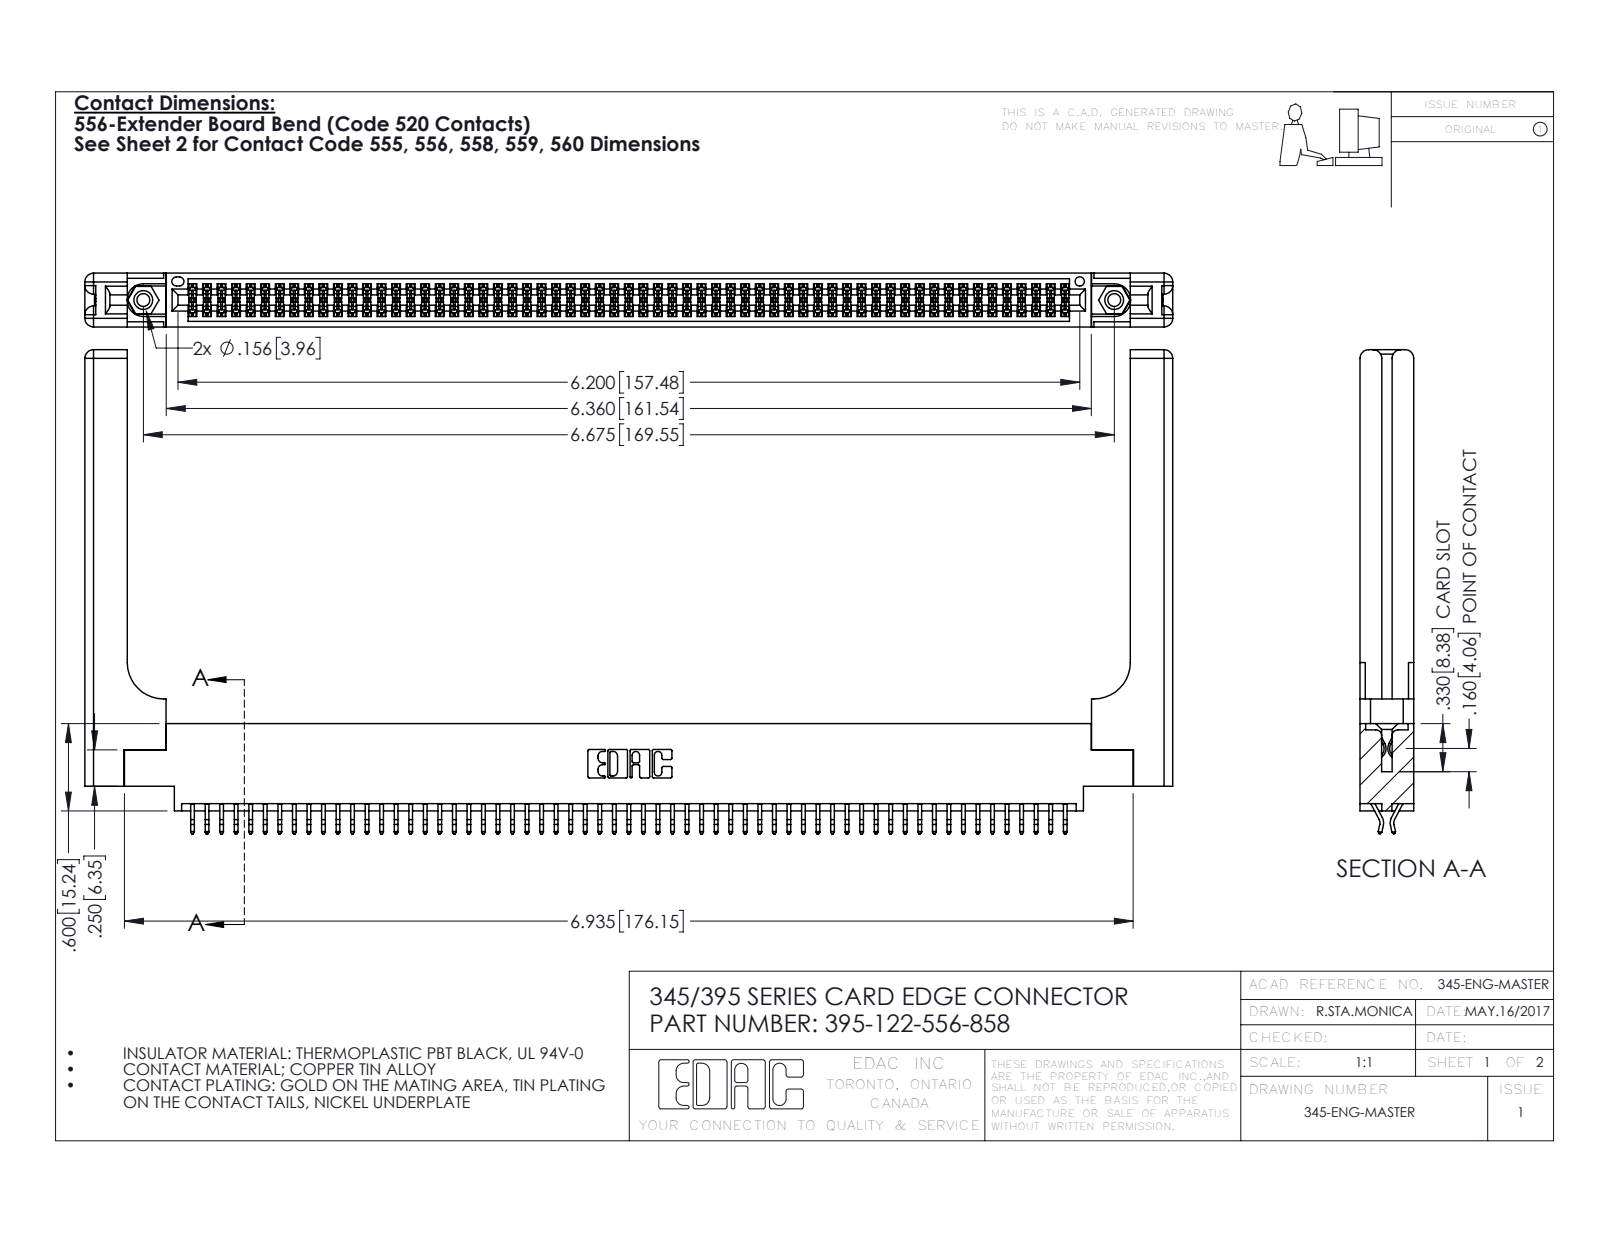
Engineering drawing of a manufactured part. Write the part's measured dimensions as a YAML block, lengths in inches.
part_name: "345-250-001_345-250-001-102; 345-292-001_556 Tail; 395-122-556-858; 345-220-058_345-220-058 (+1 more)"
step_written_by: "SolidWorks 2016 (CONFIG_CONTROL_DESIGN)"
units: inches
bodies: {solids: 127, faces: 7218, planar: 4746, cylindrical: 2412, other: 60}
overall_size: [7.479, 3.327, 0.37]
volume: 1.647
surface_area: 50.88
round_holes:
  - {diameter: 0.089, count: 2}
  - {diameter: 0.125, count: 2}
  - {diameter: 0.156, count: 2}
  - {diameter: 0.064, count: 1}
round_bosses_or_shafts:
  - {diameter: 0.155, count: 2}
partial_cylinders:
  - {radius: 0.006, count: 183}
  - {radius: 0.01, count: 22}
  - {radius: 0.06, count: 16}
  - {radius: 0.007, count: 6}
  - {radius: 0.031, count: 6}
  - {radius: 0.026, count: 3}
  - {radius: 0.01, count: 2}
  - {radius: 0.014, count: 2}
face_to_face_distances: [0.072, 0.37, 0.298, 0.025, 0.098, 0.272, 0.2, 0.225, 0.175, 0.148]
hole_center_spacings: [0.27, 6.439, 6.675]
